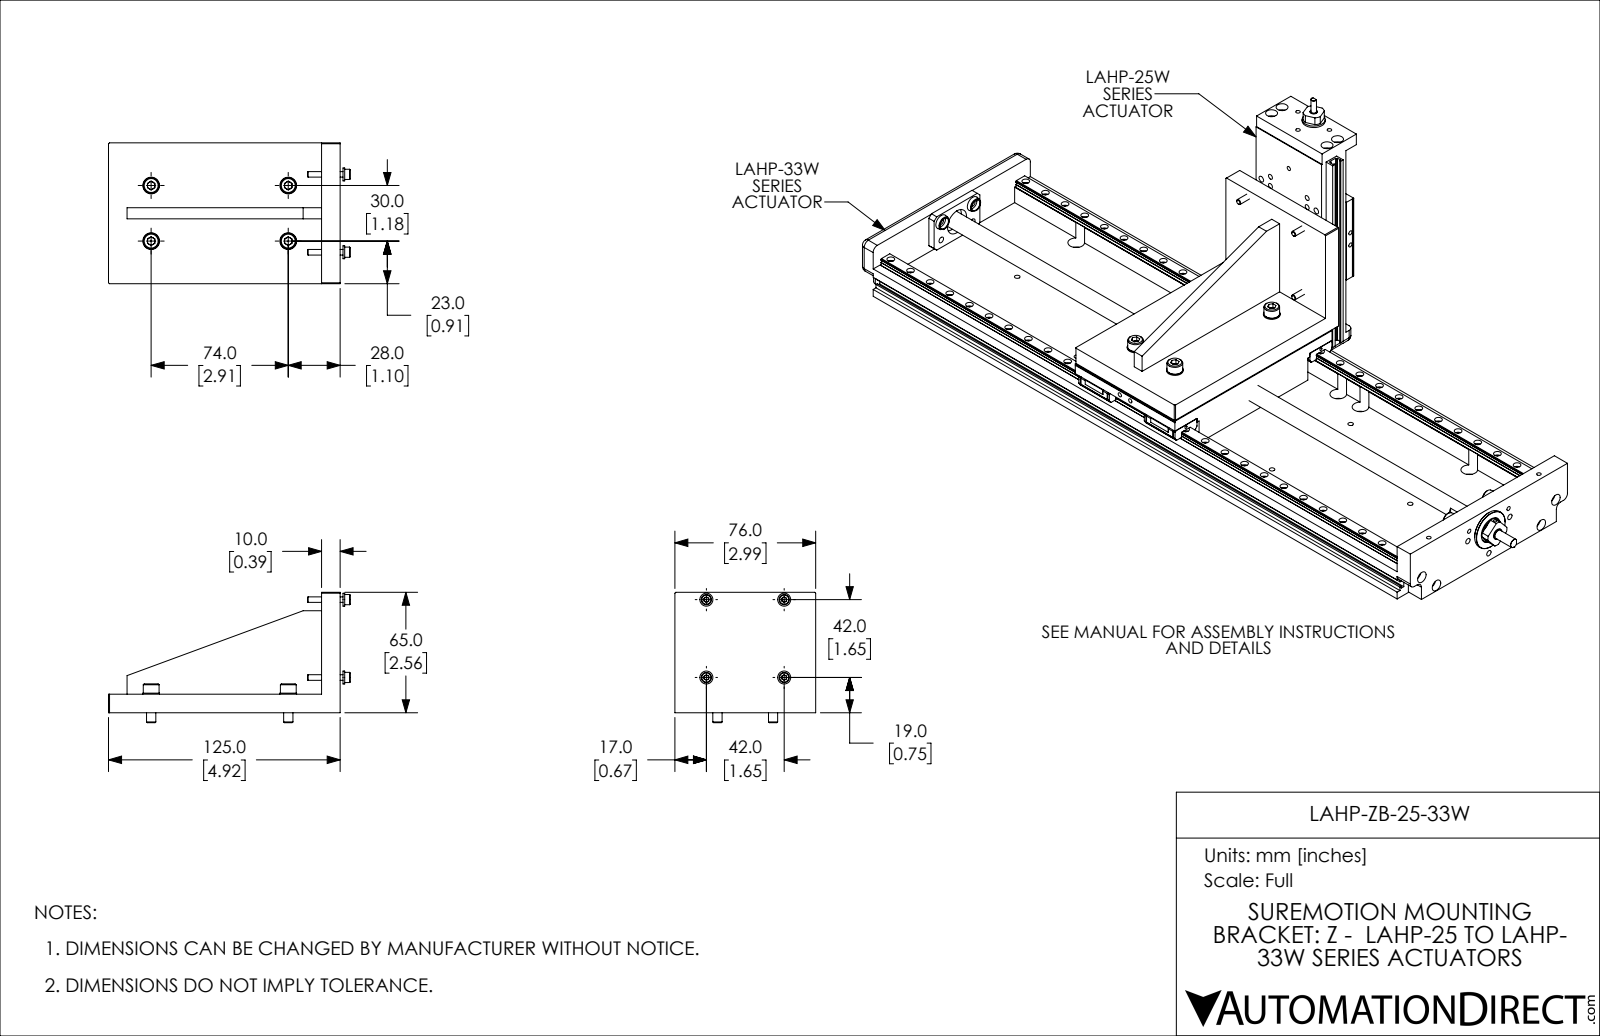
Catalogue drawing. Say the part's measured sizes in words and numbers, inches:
The part is named "LAHP-ZB-25-33W". Its 3-D file was written by "SolidWorks 2019 (CONFIG_CONTROL_DESIGN)". It is 17 solids with 297 faces: 153 planar, 80 cylindrical and 64 other. Overall it measures 5.136 by 2.992 by 2.772 inches. Its volume is 9.596 cubic inches and its surface area 67.03 square inches. Round holes: 4 of diameter 0.098, 4 of diameter 0.145, 4 of diameter 0.209, 4 of diameter 0.217. Round bosses or shafts: 4 of diameter 0.354, 4 of diameter 0.335, 4 of diameter 0.276, 4 of diameter 0.217, 4 of diameter 0.197, 4 of diameter 0.118. The main face-to-face distances are 0.394, 1.378, 1.614, 0.236, 2.992, 4.528, 2.165, 4.921, 2.559, 0.417. The hole center spacings are 1.654, 1.181, 2.339, 2.913, 3.144.
